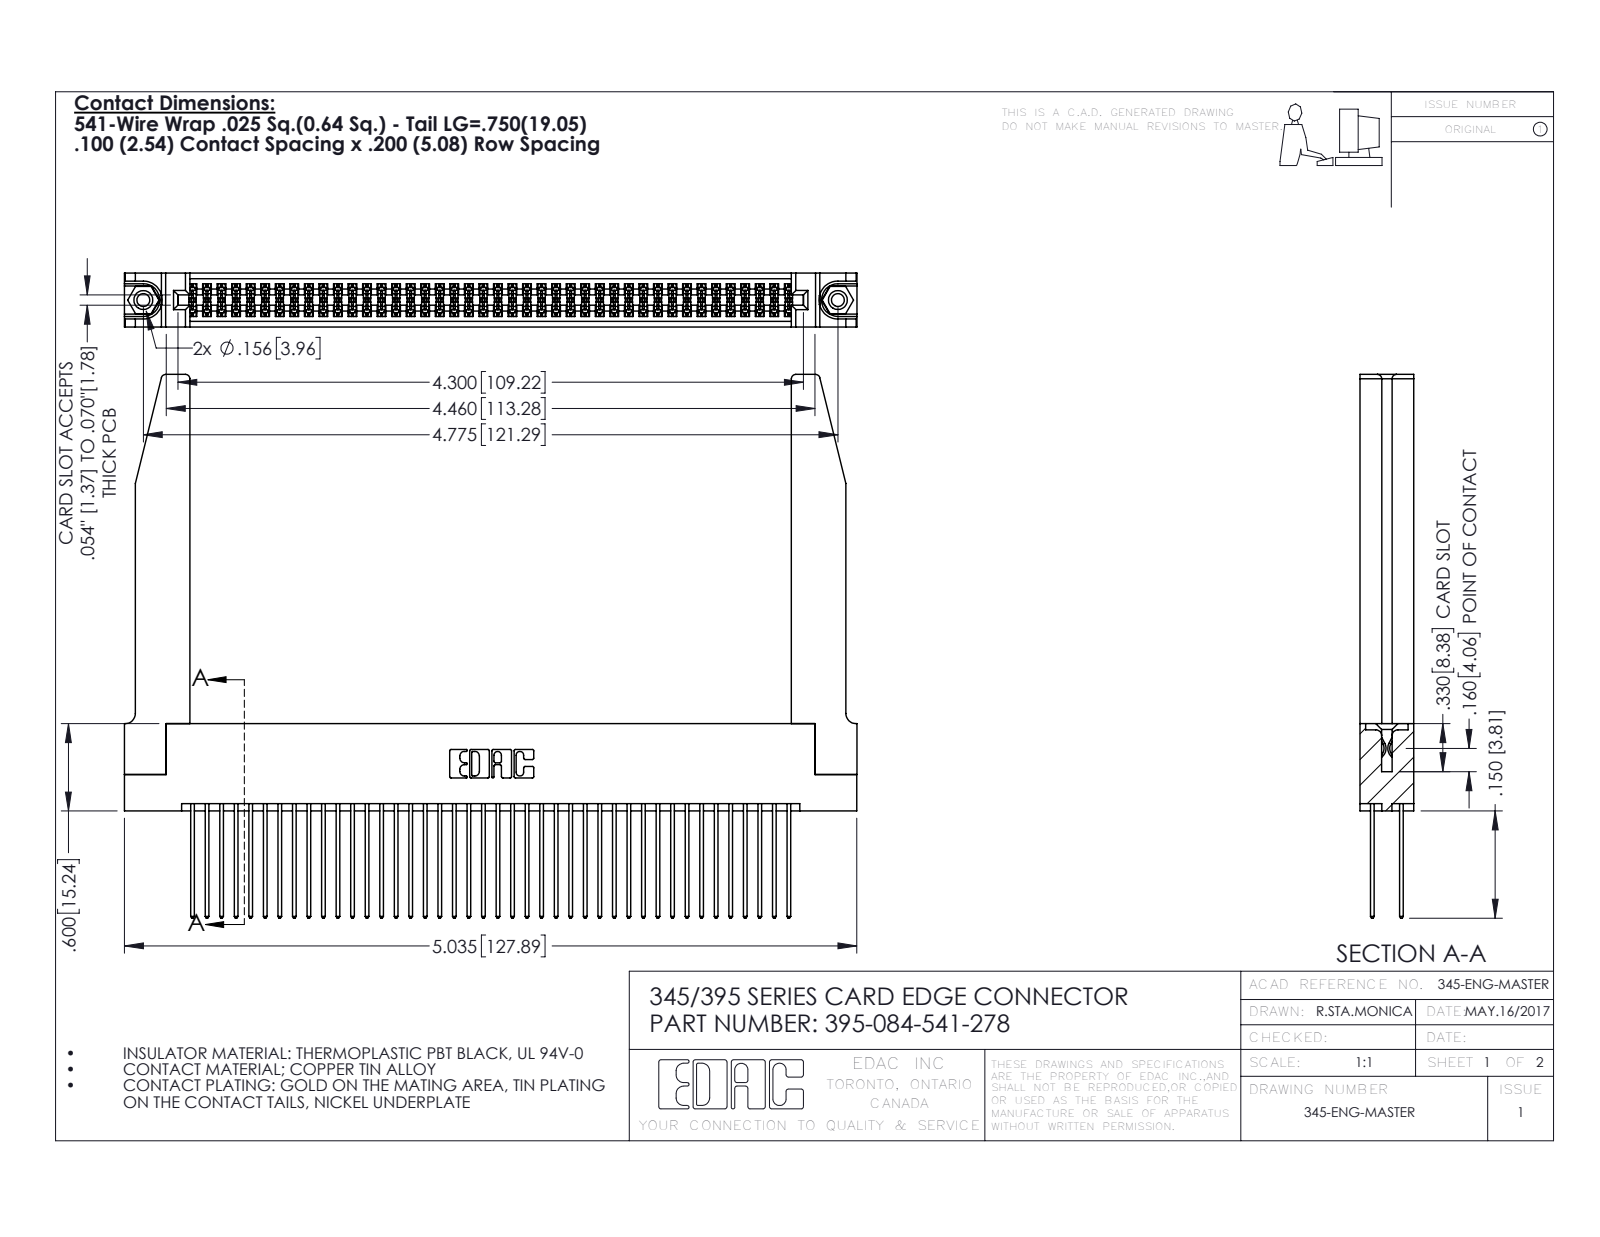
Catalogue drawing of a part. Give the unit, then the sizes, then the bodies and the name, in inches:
Units: inches
Overall size (bounding box): 5.036 × 3.737 × 0.37
Round holes (diameter × count): ⌀0.089 ×2, ⌀0.125 ×2, ⌀0.156 ×2, ⌀0.064 ×1
Round bosses / shafts (diameter × count): ⌀0.155 ×2
Partial cylindrical surfaces — rounded edges, fillets, slot ends (radius × count): R0.006 ×126, R0.01 ×84, R0.01 ×22, R0.03 ×8, R0.007 ×6, R0.031 ×6, R0.026 ×3, R0.014 ×2
Main face-to-face distances: 0.072, 0.298, 0.37, 0.2, 0.098, 0.272, 0.025, 0.225, 0.175, 0.148
Hole centre spacings: 0.27, 4.539, 4.775
Volume: 1.262 in³ · Surface area: 43.68 in²
Bodies: 89 solids, 4560 faces (2994 planar, 1514 cylindrical, 52 other)
Part name (STEP PRODUCT): 345 Part_Flush Mounting Lugs - 0.156 Dia-TH; 345-250-001_345-250-001-102; 395-084-541-278; 345-292-001_345-293-141 (+1 more)
STEP written by: SolidWorks 2016 (CONFIG_CONTROL_DESIGN)
